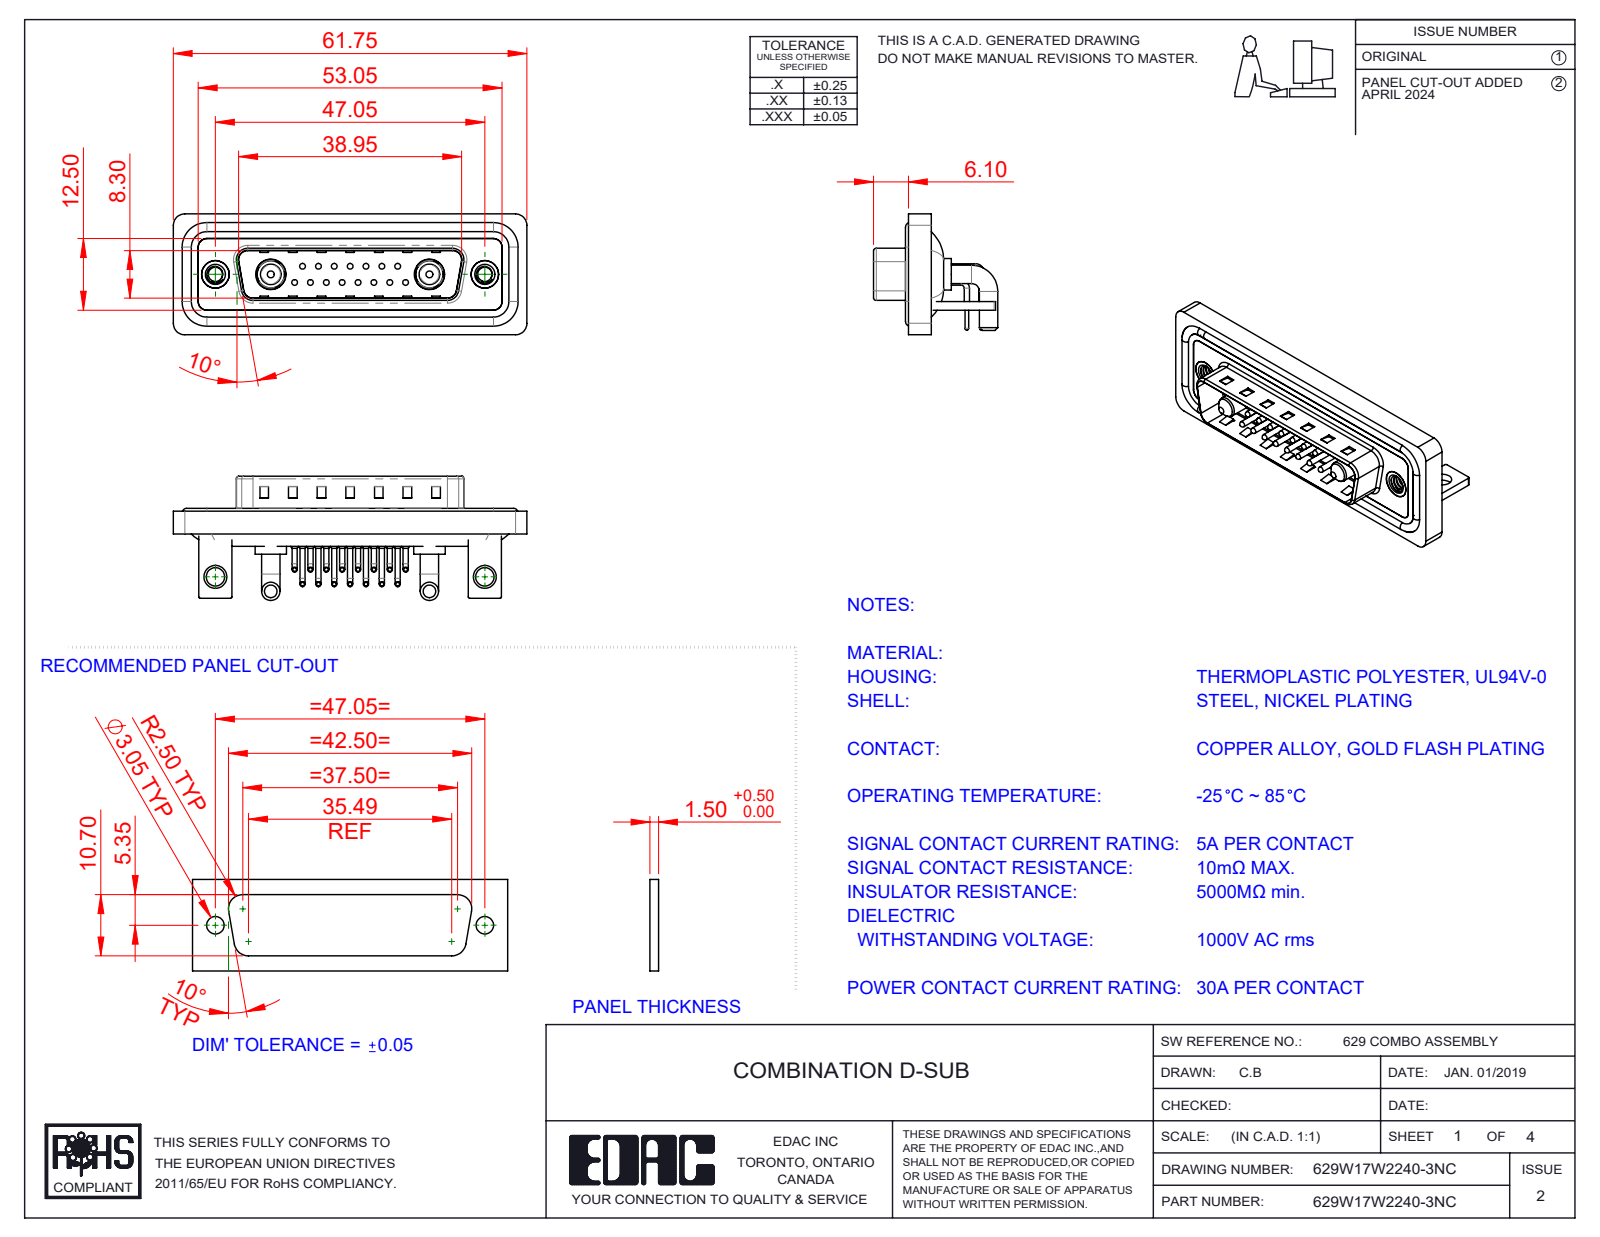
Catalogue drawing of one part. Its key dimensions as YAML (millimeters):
part_name: "629Combo Waterproof Housing_25 Contacts; 629Combo Shell Front_25 Contacts; Power Pin_30A RA; 629Combo Shell Rear_25 Contacts (+6 more)"
step_written_by: "SolidWorks 2023 (CONFIG_CONTROL_DESIGN)"
units: millimeters
bodies: {solids: 28, faces: 2257, planar: 1209, cylindrical: 788, other: 260}
overall_size: [61.75, 21.7, 21.1]
volume: 7840
surface_area: 13226
round_holes:
  - {diameter: 0.75, count: 15}
  - {diameter: 1.6, count: 15}
  - {diameter: 2, count: 15}
  - {diameter: 2.5, count: 2}
  - {diameter: 3.2, count: 2}
  - {diameter: 4, count: 2}
  - {diameter: 4.8, count: 2}
  - {diameter: 4.85, count: 2}
  - {diameter: 5, count: 2}
  - {diameter: 5.3, count: 2}
round_bosses_or_shafts:
  - {diameter: 0.9, count: 30}
  - {diameter: 1.5, count: 15}
  - {diameter: 1, count: 15}
  - {diameter: 0.65, count: 15}
  - {diameter: 3.2, count: 4}
  - {diameter: 1.6, count: 4}
  - {diameter: 5.5, count: 2}
  - {diameter: 5.2, count: 2}
partial_cylinders:
  - {radius: 2, count: 19}
  - {radius: 1.5, count: 18}
  - {radius: 0.25, count: 16}
  - {radius: 1.01, count: 15}
  - {radius: 0.5, count: 9}
  - {radius: 1.6, count: 8}
  - {radius: 0.6, count: 4}
  - {radius: 0.65, count: 4}
face_to_face_distances: [0.4, 0.8, 1.5, 2.1, 2.9, 1.1, 4.1, 1.6, 4.5, 3.7]
hole_center_spacings: [3.16, 2.77, 5.54, 8.31, 5.04, 7.49, 11.08, 5.03]
